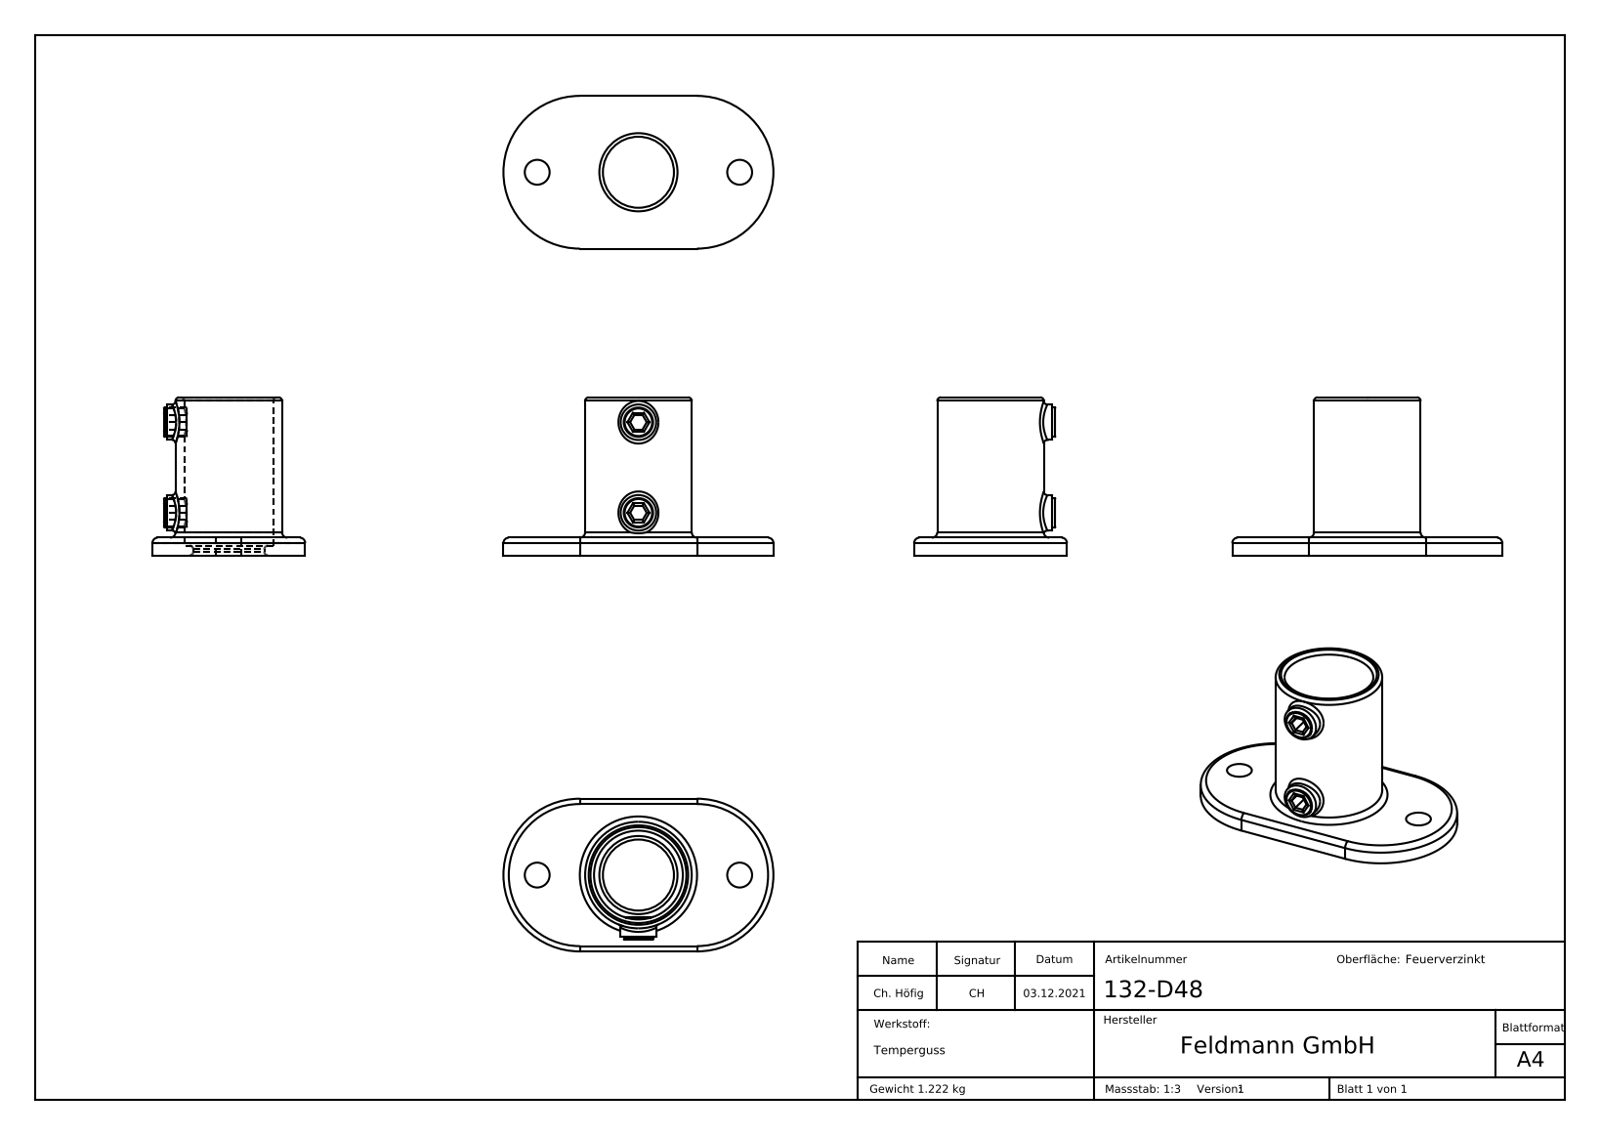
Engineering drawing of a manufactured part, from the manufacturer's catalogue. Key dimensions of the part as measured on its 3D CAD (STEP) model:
Part name (STEP PRODUCT): 132-D48; 132-D48 Teil2; 132-D48 Teil1
STEP written by: SolidWorks 2018 (CONFIG_CONTROL_DESIGN)
Units: millimetres
Bodies: 3 solids, 77 faces (24 planar, 40 cylindrical, 13 other)
Overall size (bounding box): 152 × 89 × 86
Volume: 166 995 mm³ · Surface area: 55 616 mm²
Round holes (diameter × count): ⌀14 ×2, ⌀15.25 ×2, ⌀40 ×1, ⌀50 ×1
Round bosses / shafts (diameter × count): ⌀20 ×2, ⌀16.5 ×2, ⌀60 ×1
Partial cylindrical surfaces — rounded edges, fillets, slot ends (radius × count): R2 ×24, R3 ×2, R43 ×2
Main face-to-face distances: 10, 86, 5.5, 4.5, 8.1, 77.5, 8.5, 25.5, 66.5, 11
Hole centre spacings: 57, 51, 114
